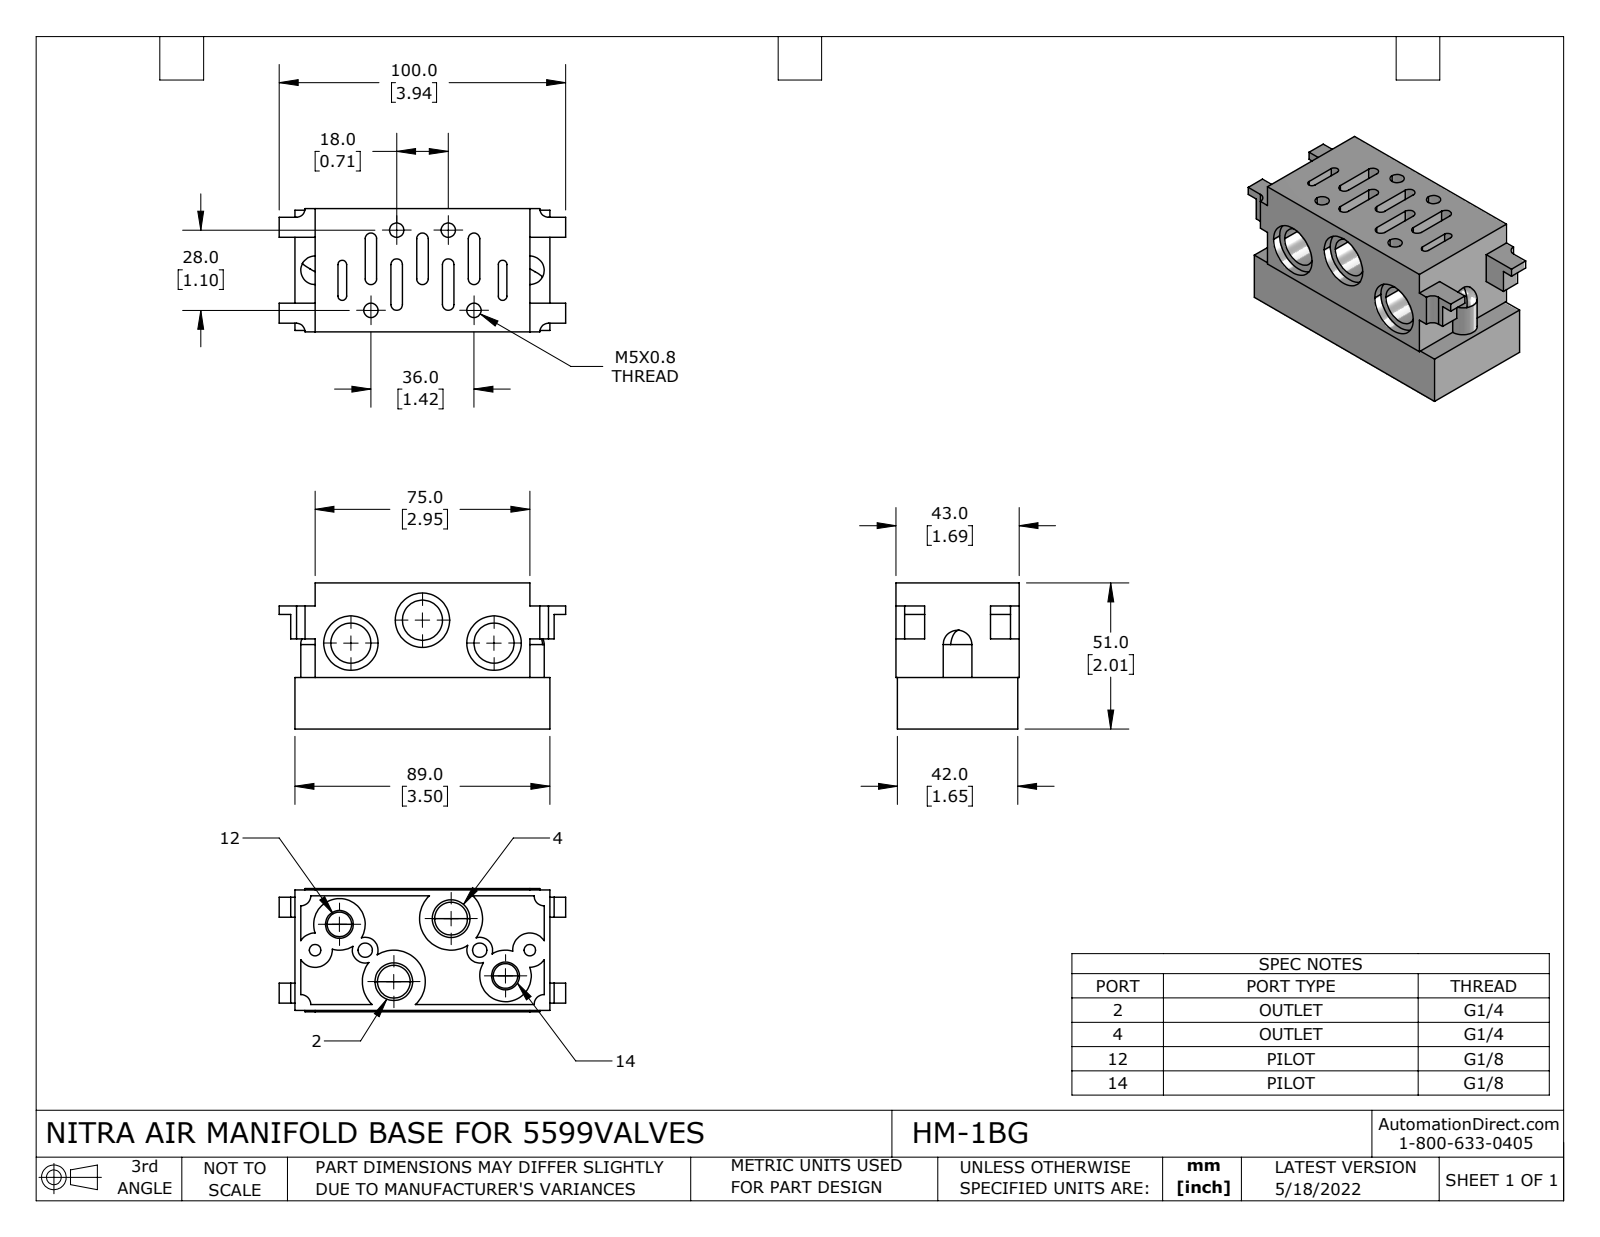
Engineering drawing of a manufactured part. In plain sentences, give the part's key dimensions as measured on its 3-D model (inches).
The part is named "HM-1BG". Its 3-D file was written by "SolidWorks 2021 (CONFIG_CONTROL_DESIGN)". It is 1 solid with 181 faces: 85 planar, 76 cylindrical and 20 other. Overall it measures 3.937 by 2.008 by 1.693 inches. Its volume is 7.605 cubic inches and its surface area 58.9 square inches. Round holes: 6 of diameter 0.197, 3 of diameter 0.551, 3 of diameter 0.748, 2 of diameter 0.157, 2 of diameter 0.337, 2 of diameter 0.451. Partial cylindrical surfaces (rounded edges, fillets, slot ends): 10 of radius 0.079, 4 of radius 0.059, 4 of radius 0.118, 4 of radius 0.138, 2 of radius 0.177, 2 of radius 0.197, 2 of radius 0.236, 2 of radius 0.354. The main face-to-face distances are 0.02, 1.673, 1.575, 0.079, 0.098, 1.693, 1.594, 1.457, 0.276, 0.551. The hole center spacings are 1.033, 0.487, 0.501, 0.557, 0.585, 0.689, 0.701, 0.945.
